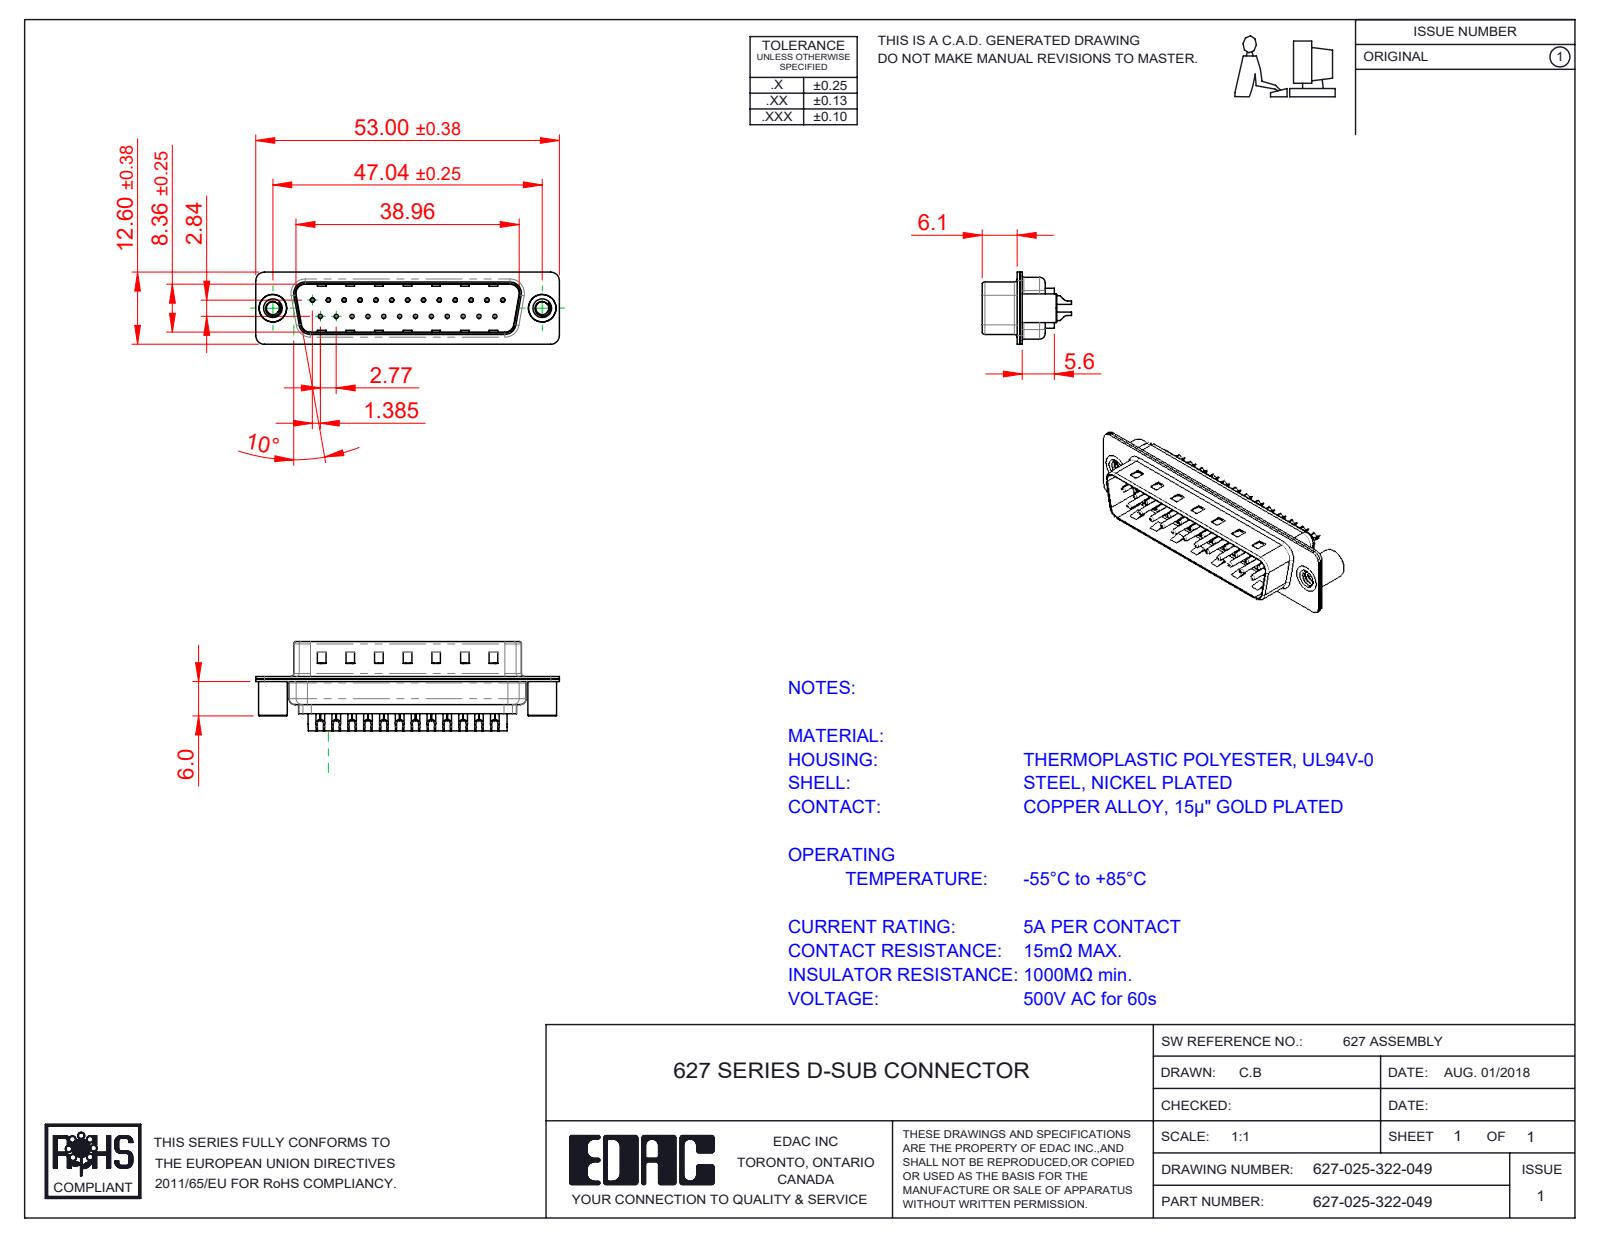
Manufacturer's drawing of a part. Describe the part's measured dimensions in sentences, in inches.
The part is named "627 4-40 Threaded Standoff BS; 627 Contact Row 1_22L; 627 Shell Rear_25 Contacts; 627-025-322-049 (+3 more)". Its 3-D file was written by "SolidWorks 2020 (CONFIG_CONTROL_DESIGN)". It is 30 solids with 1998 faces: 521 planar, 882 cylindrical and 595 other. Overall it measures 2.087 by 0.604 by 0.496 inches. Its volume is 0.17 cubic inches and its surface area 12.47 square inches. Round holes: 25 of diameter 0.014, 25 of diameter 0.043, 25 of diameter 0.063, 2 of diameter 0.089, 2 of diameter 0.157, 2 of diameter 0.189. Round bosses or shafts: 25 of diameter 0.079, 25 of diameter 0.059, 25 of diameter 0.03, 2 of diameter 0.197, 2 of diameter 0.193. Partial cylindrical surfaces (rounded edges, fillets, slot ends): 16 of radius 0.059, 12 of radius 0.079, 8 of radius 0.02, 8 of radius 0.063, 6 of radius 0.039, 4 of radius 0.01, 4 of radius 0.024, 4 of radius 0.026. The main face-to-face distances are 0.016, 0.018, 0.032, 0.377, 0.345, 0.035, 0.059, 0.256, 0.055, 0.238. The hole center spacings are 0.124, 0.327, 0.109, 0.218, 0.436, 0.654, 0.198, 0.198.
